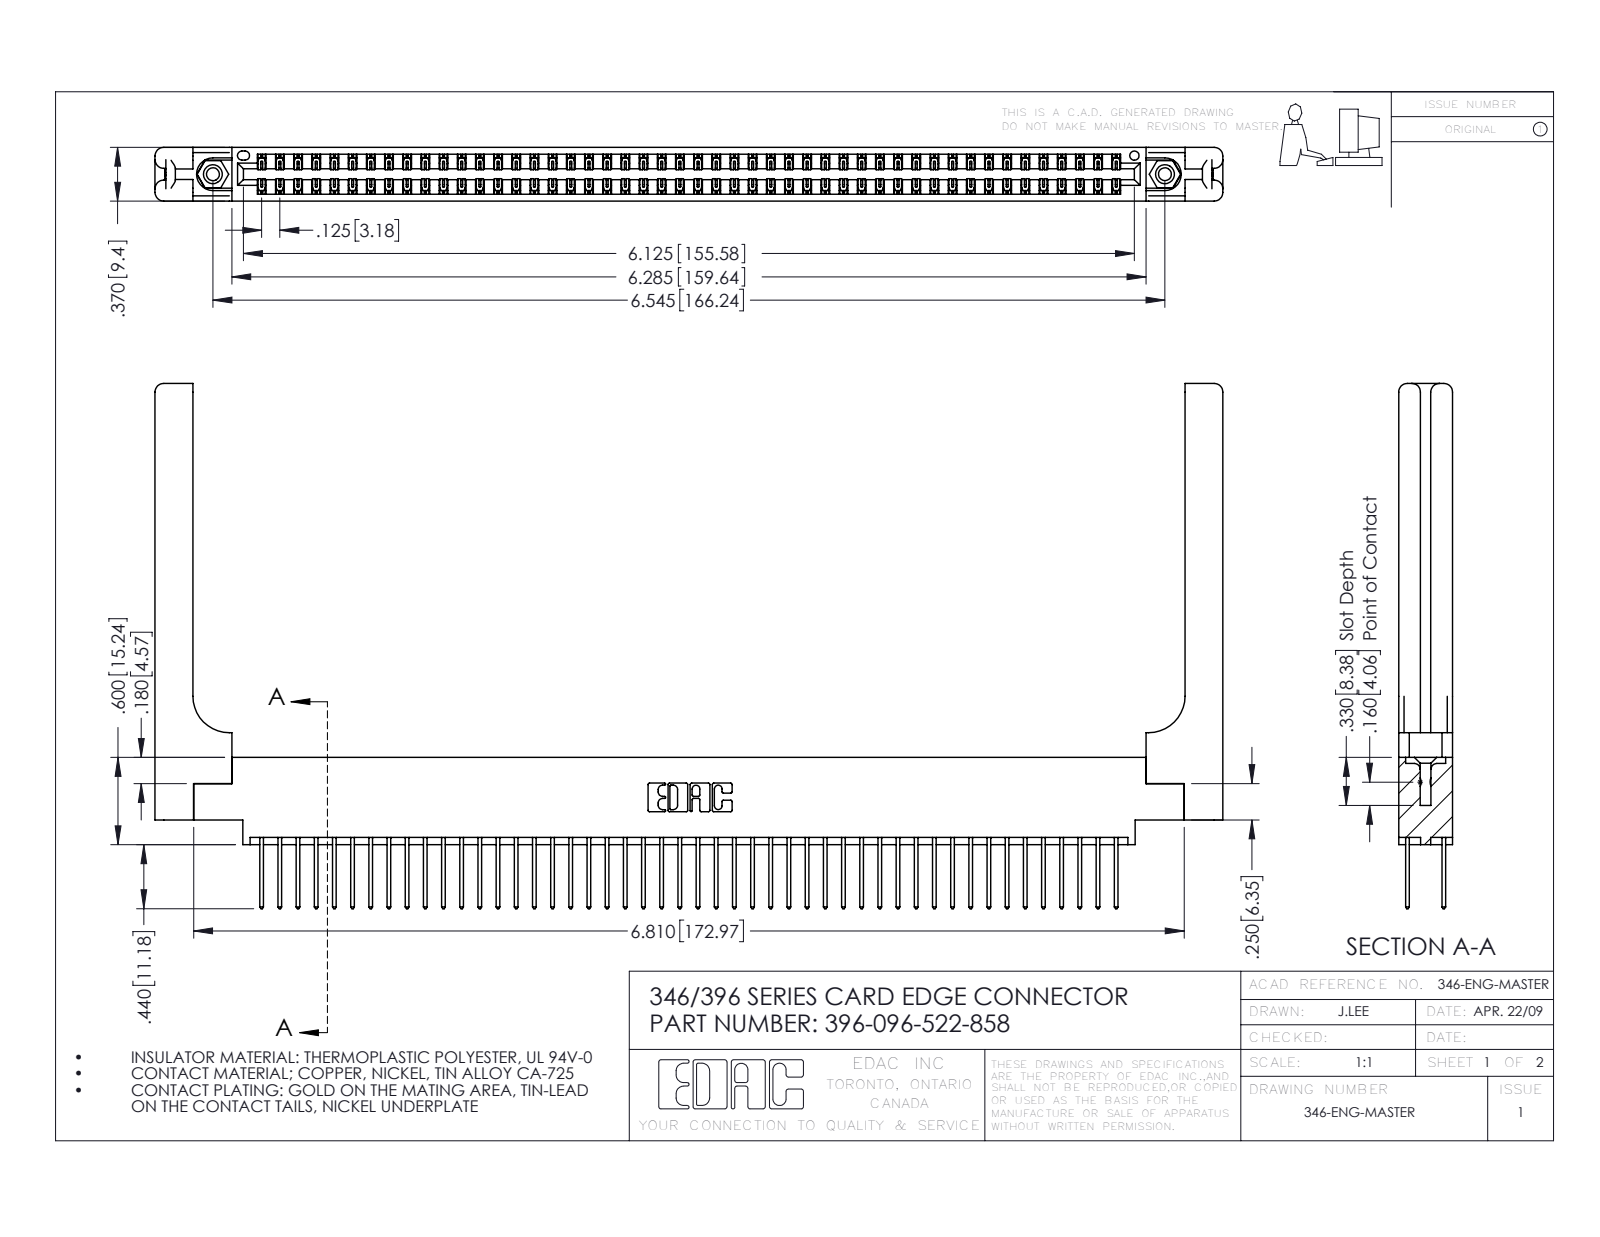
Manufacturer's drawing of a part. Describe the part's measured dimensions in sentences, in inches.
The part is named "345-292-001_345-293-122; 346 Part_0.170 Offset - 0.156 Dia-TH; 396-096-522-858; 345-250-001_345-250-001-102 (+1 more)". Its 3-D file was written by "SolidWorks 2016 (CONFIG_CONTROL_DESIGN)". It is 101 solids with 5374 faces: 3588 planar, 1726 cylindrical and 60 other. Overall it measures 7.341 by 3.61 by 0.37 inches. Its volume is 1.575 cubic inches and its surface area 48.93 square inches. Round holes: 2 of diameter 0.089, 2 of diameter 0.125, 2 of diameter 0.156, 1 of diameter 0.064. Round bosses or shafts: 2 of diameter 0.155. Partial cylindrical surfaces (rounded edges, fillets, slot ends): 144 of radius 0.006, 96 of radius 0.01, 22 of radius 0.01, 16 of radius 0.06, 6 of radius 0.007, 6 of radius 0.031, 3 of radius 0.026, 2 of radius 0.014. The main face-to-face distances are 0.048, 0.322, 0.37, 0.072, 0.25, 0.025, 0.298, 0.148, 0.15, 0.275. The hole center spacings are 0.246, 6.336, 6.545.
